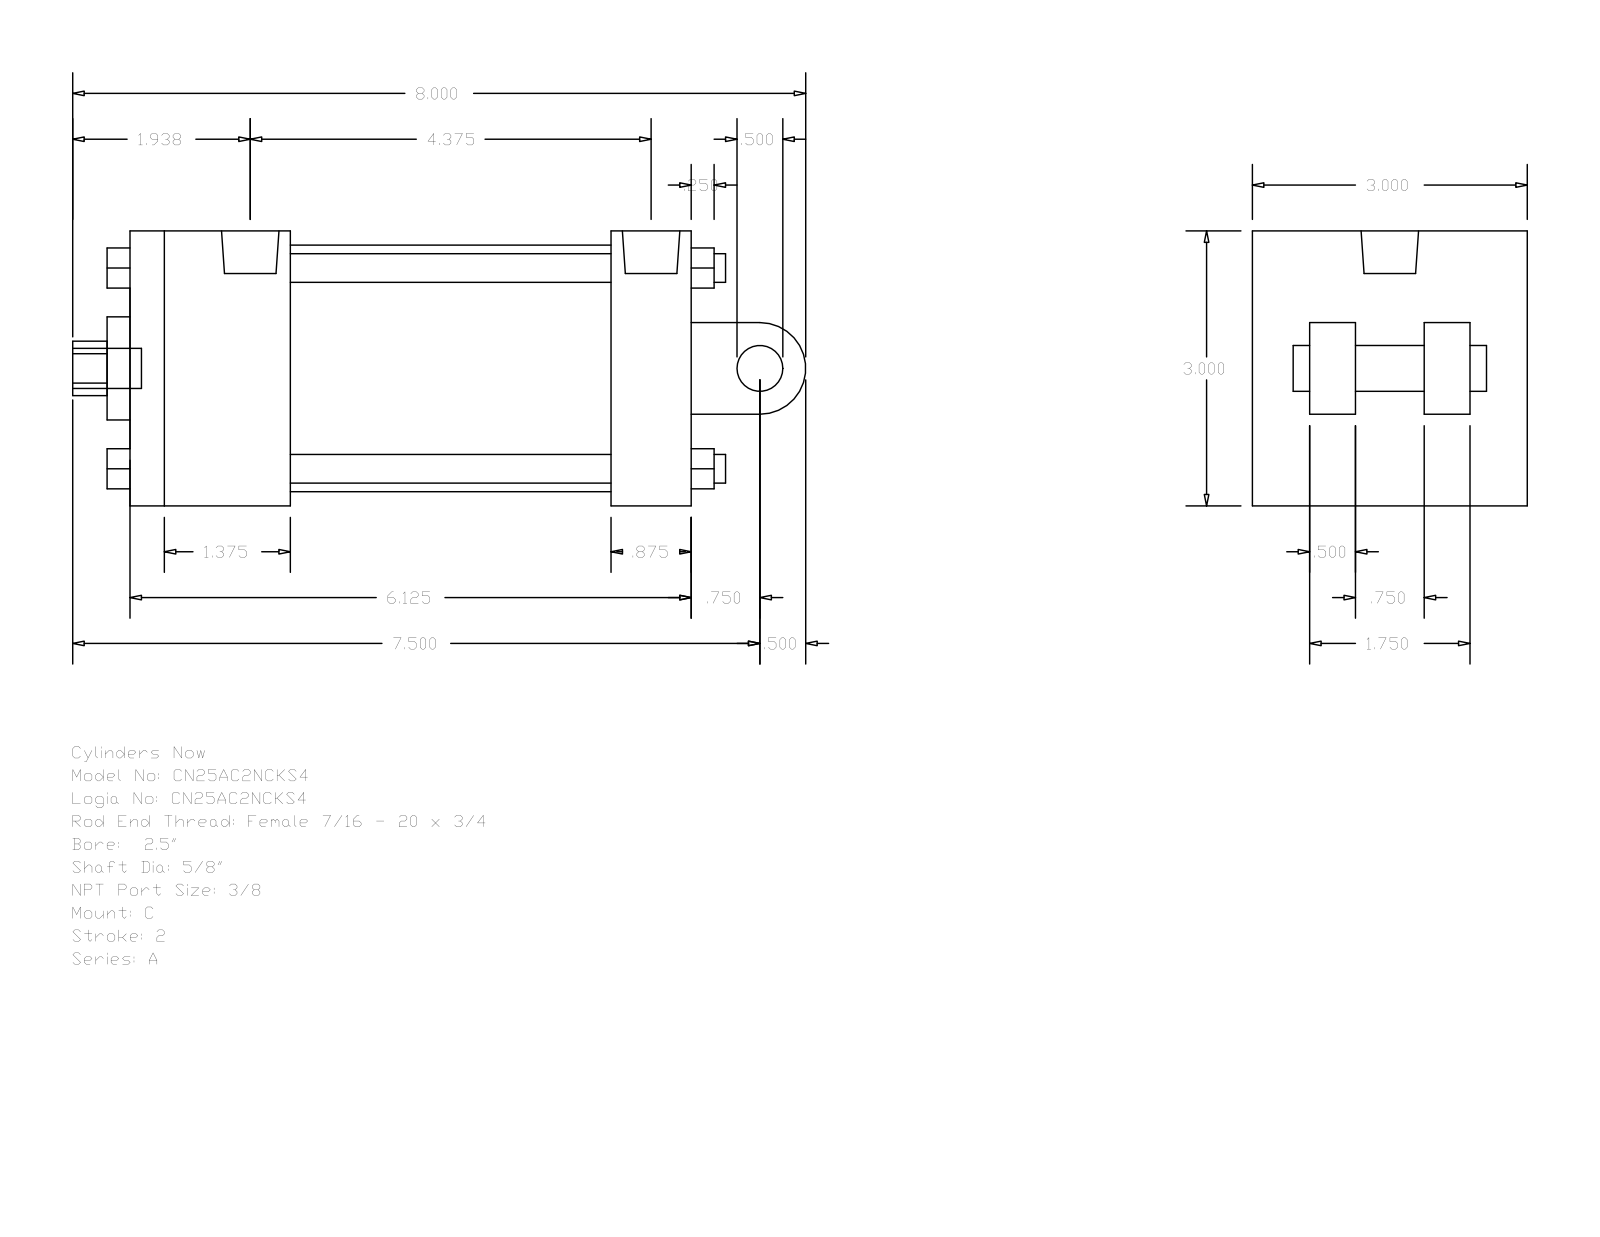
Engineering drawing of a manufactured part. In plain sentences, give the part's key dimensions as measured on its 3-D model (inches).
The part is named "A_C__0250_0.625". Its 3-D file was written by "GSSL Pune (CONFIG_CONTROL_DESIGN)". It is 0 solids with 135 faces: 102 planar, 33 cylindrical and 0 other. Overall it measures 8 by 3 by 3 inches. Round holes: 2 of diameter 0.219, 1 of diameter 0.625, 1 of diameter 0.627, 1 of diameter 1.125, 1 of diameter 2.69. Round bosses or shafts: 4 of diameter 0.313, 2 of diameter 0.219, 1 of diameter 0.627, 1 of diameter 0.5, 1 of diameter 0.437. Partial cylindrical surfaces (rounded edges, fillets, slot ends): 1 of radius 0.297, 1 of radius 0.5. The main face-to-face distances are 3, 6.125, 1.75, 5.25, 3.5, 4.375, 0.875, 2, 0.5, 0.625. The hole center spacings are 0.094.
